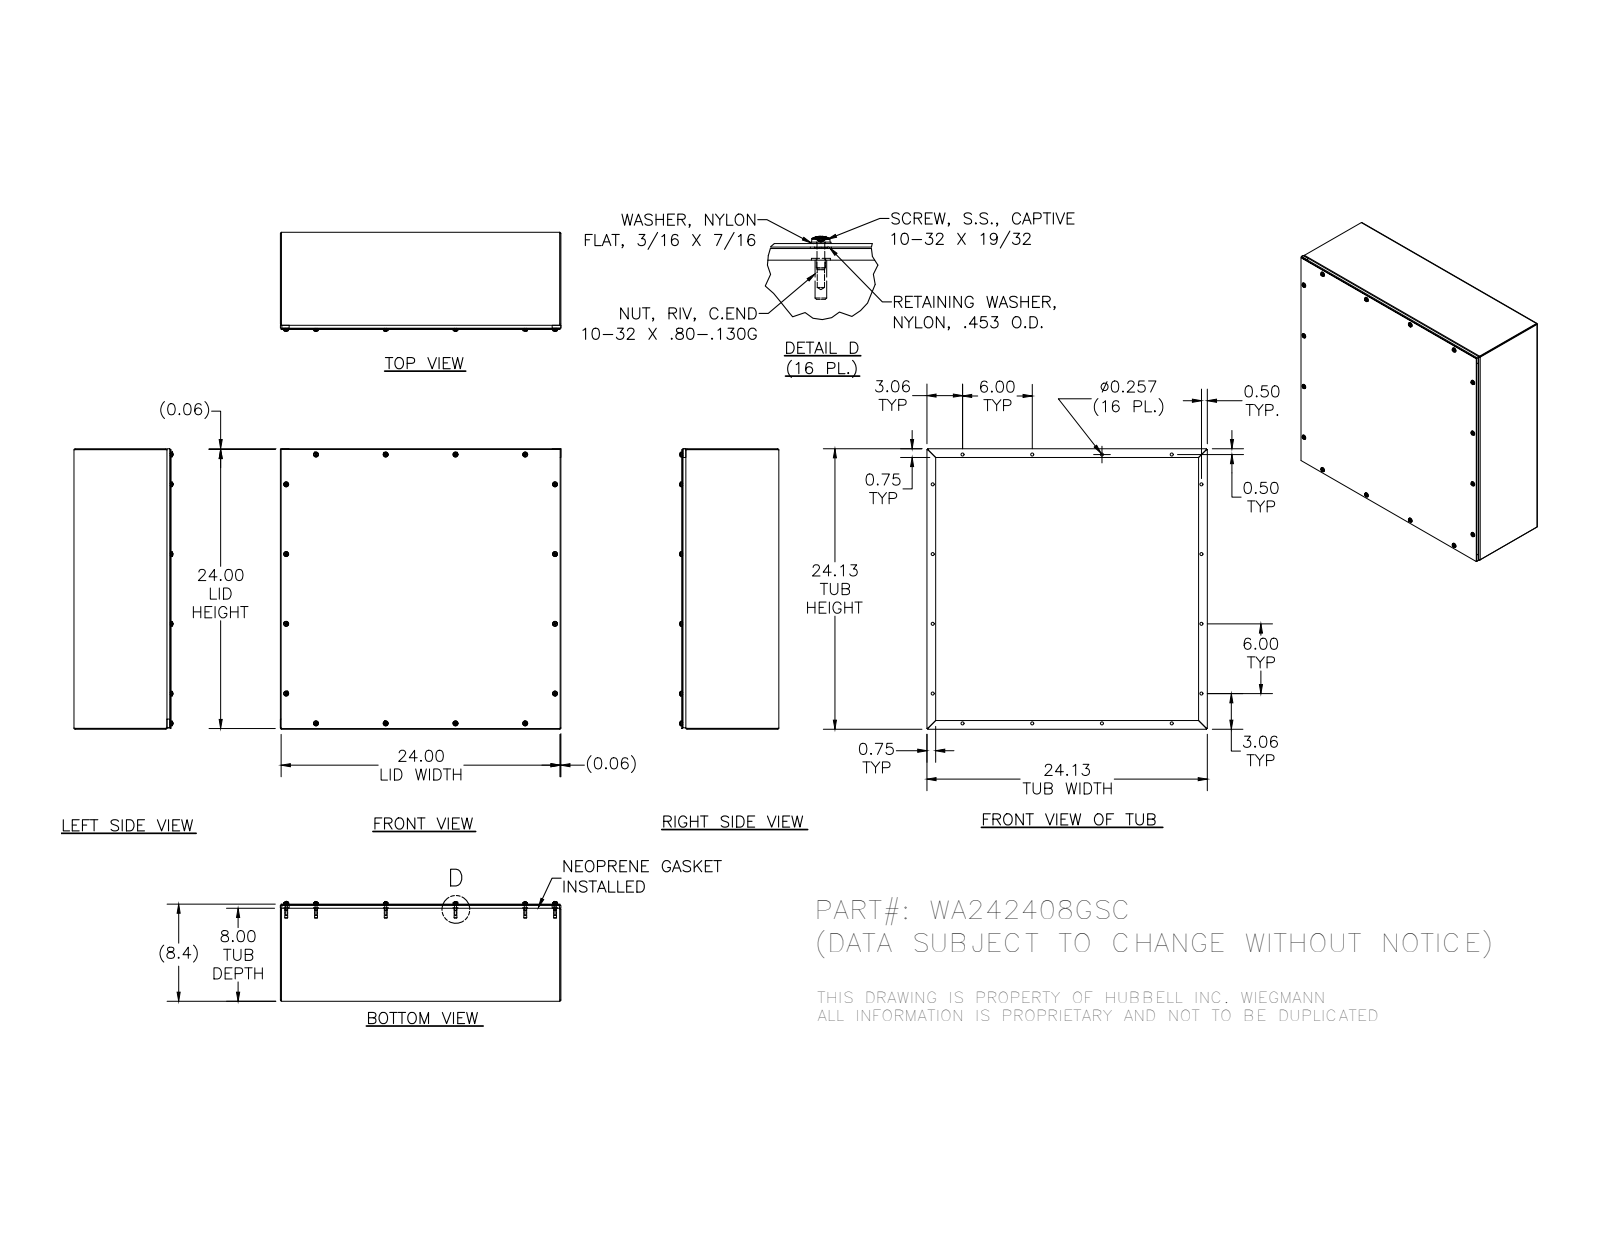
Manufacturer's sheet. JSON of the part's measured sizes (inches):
{"part_name": "39035; 39077; 34984; WA242408GSCBKP (+3 more)", "step_written_by": "SolidWorks 2014 (AUTOMOTIVE_DESIGN)", "units": "inches", "bodies": {"solids": 69, "faces": 1646, "planar": 766, "cylindrical": 432, "other": 448}, "overall_size": [24.125, 24.125, 8.511], "volume_in3": 160.5, "surface_area_in2": 4156, "round_holes": [[0.188, 16], [0.257, 16], [0.278, 16], [0.281, 16], [0.156, 15], [0.196, 15]], "round_bosses_or_shafts": [[0.453, 16], [0.437, 16], [0.167, 16], [0.406, 15], [0.248, 15]], "partial_cylinders_radius": [[0.089, 16], [0.031, 8], [0.105, 8]], "face_to_face_distances": [0.074, 8.282, 24.051, 8.356, 8.208, 24.125, 23.977, 0.356, 7.926, 0.282], "hole_center_spacings": [6, 12, 25.197, 26.053, 8.938, 14.786, 20.722, 22.274]}
